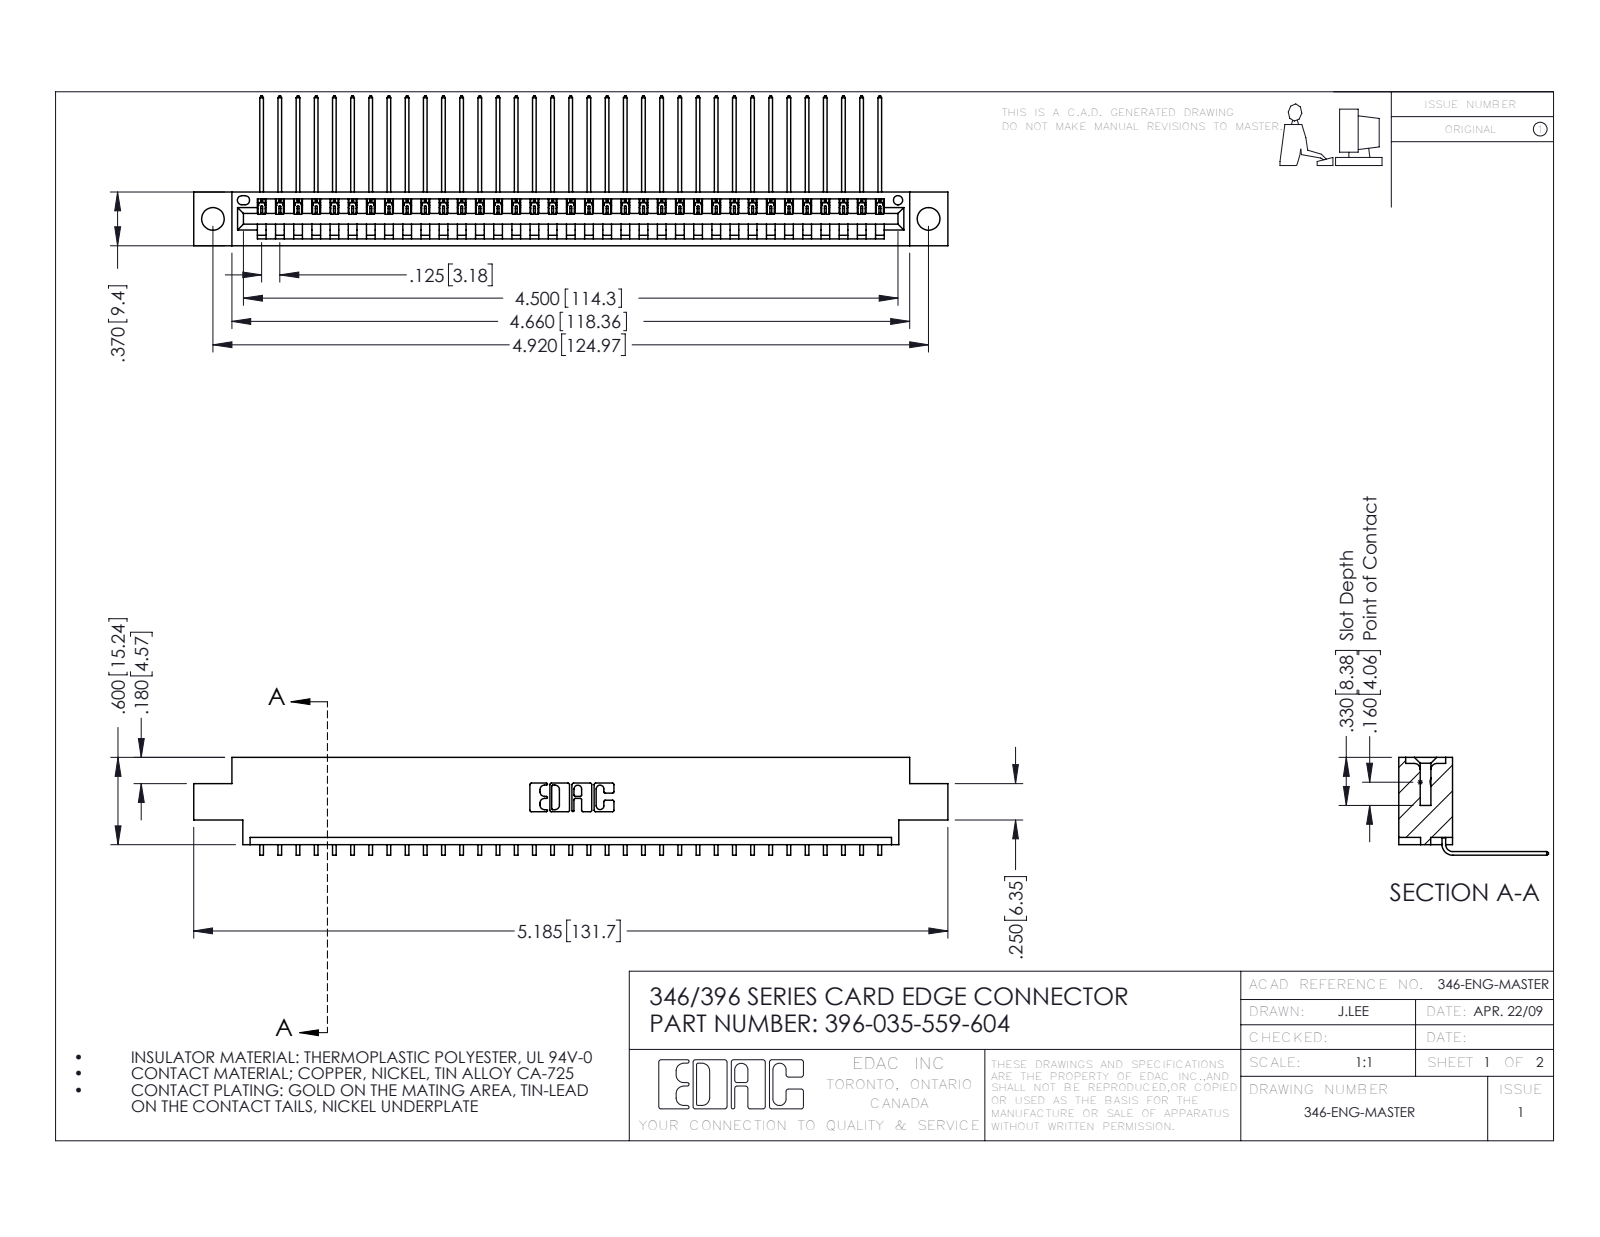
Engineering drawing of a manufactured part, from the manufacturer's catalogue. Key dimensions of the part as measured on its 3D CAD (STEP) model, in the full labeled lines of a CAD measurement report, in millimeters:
Part name (STEP PRODUCT): 396-035-559-604; 346 Part_0.170 Offset - 0.156 Dia-TH; 345-292-001_558 559 Tail - 1
STEP written by: SolidWorks 2016 (CONFIG_CONTROL_DESIGN)
Units: millimetres
Bodies: 36 solids, 2226 faces (1550 planar, 676 cylindrical, 0 other)
Overall size (bounding box): 131.7 × 26.2 × 17.1
Volume: 12 400 mm³ · Surface area: 16 120 mm²
Round holes (diameter × count): ⌀4 ×2, ⌀1.6 ×1
Partial cylindrical surfaces — rounded edges, fillets, slot ends (radius × count): R0.2 ×70, R0.3 ×22, R0.2 ×6, R0.8 ×6, R0.7 ×3, R0.8 ×2, R1 ×2, R0.4 ×1
Main face-to-face distances: 1.2, 8.2, 9.4, 0.6, 6.4, 1.8, 7.6, 3.8, 5.6, 2.5
Hole centre spacings: 6.2, 119.7, 125
